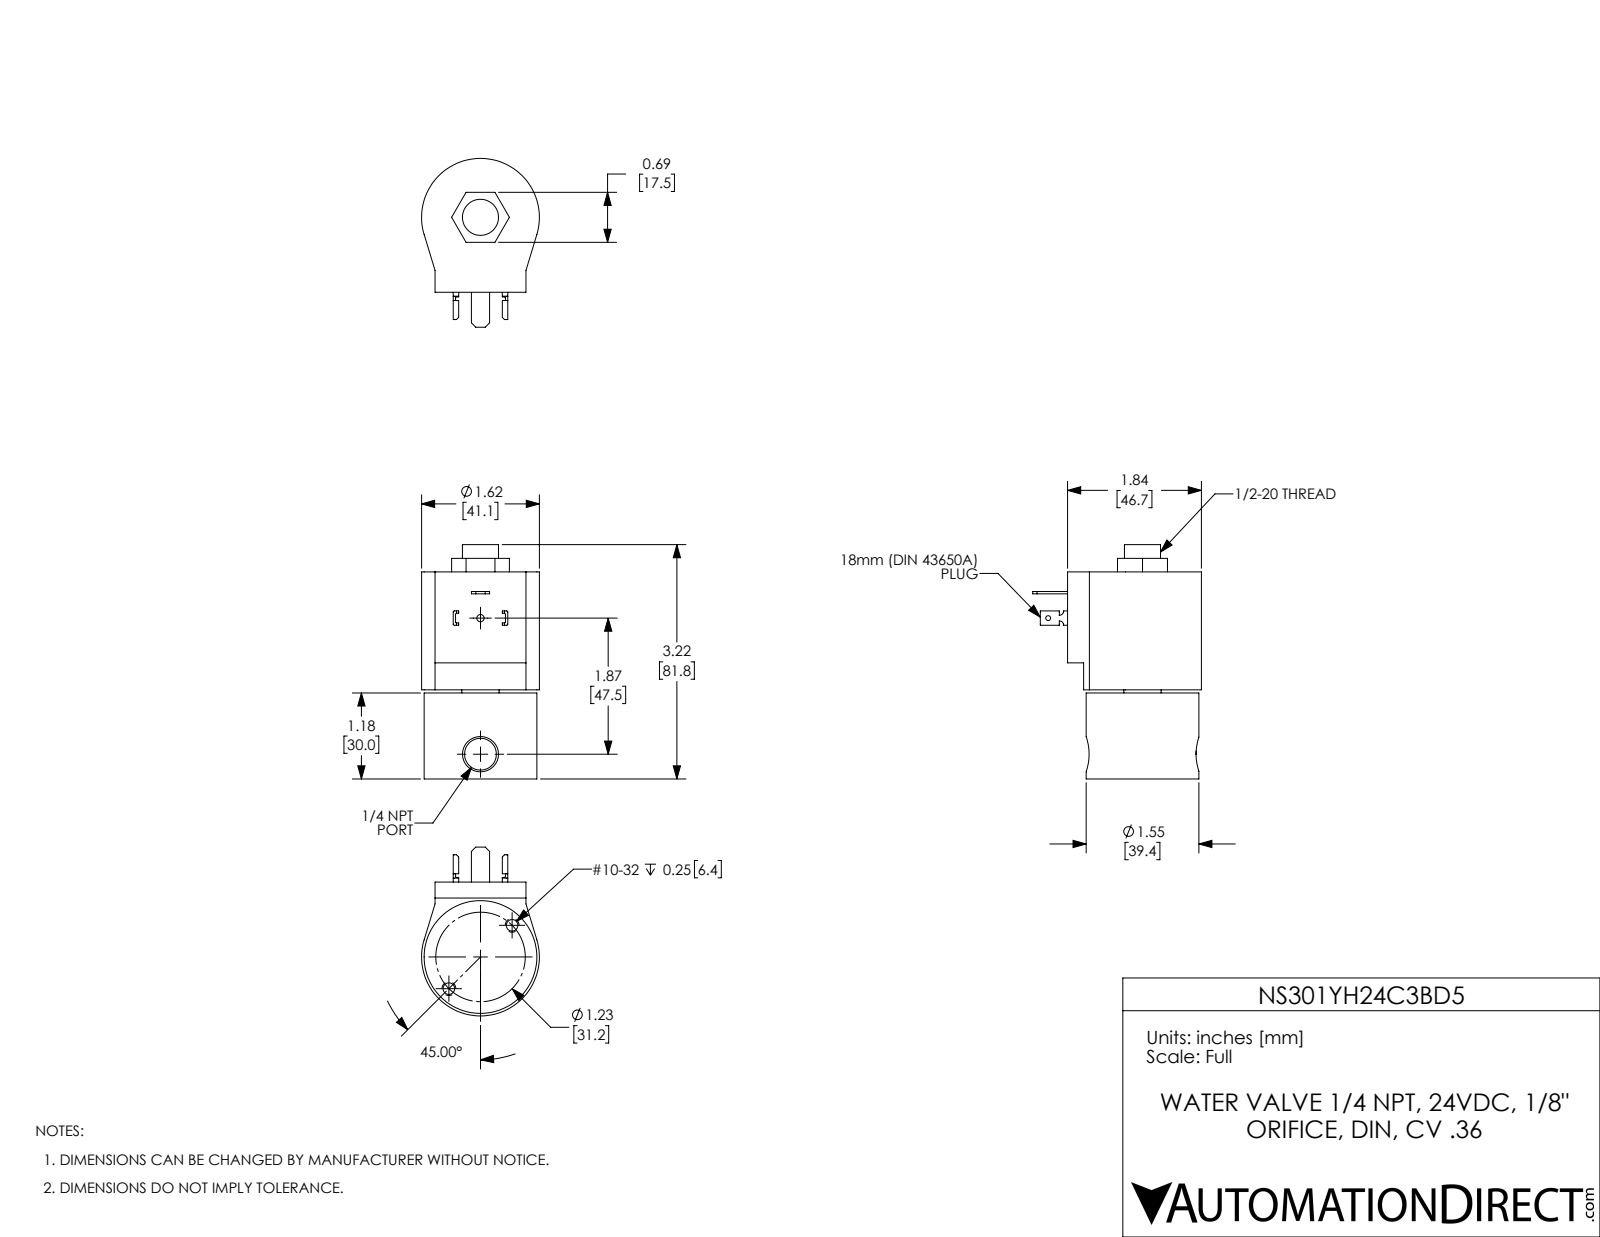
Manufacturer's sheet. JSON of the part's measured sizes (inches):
{"part_name": "NS301YH16C3BD5", "step_written_by": "SolidWorks 2024 (CONFIG_CONTROL_DESIGN)", "units": "inches", "bodies": {"solids": 6, "faces": 130, "planar": 73, "cylindrical": 49, "other": 8}, "overall_size": [3.22, 2.32, 1.62], "volume_in3": 6.042, "surface_area_in2": 33.19, "round_holes": [[0.159, 2], [0.067, 1], [0.1, 1], [0.437, 1], [0.496, 1], [0.512, 1], [1.155, 1]], "round_bosses_or_shafts": [[1.55, 1]], "partial_cylinders_radius": [[0.015, 8], [0.06, 2], [0.81, 1]], "face_to_face_distances": [2.845, 1.182, 1.663, 1.225, 0.043, 1.62, 1.287, 0.106, 0.062, 1.558], "hole_center_spacings": [0.615, 1.23, 1.87]}
